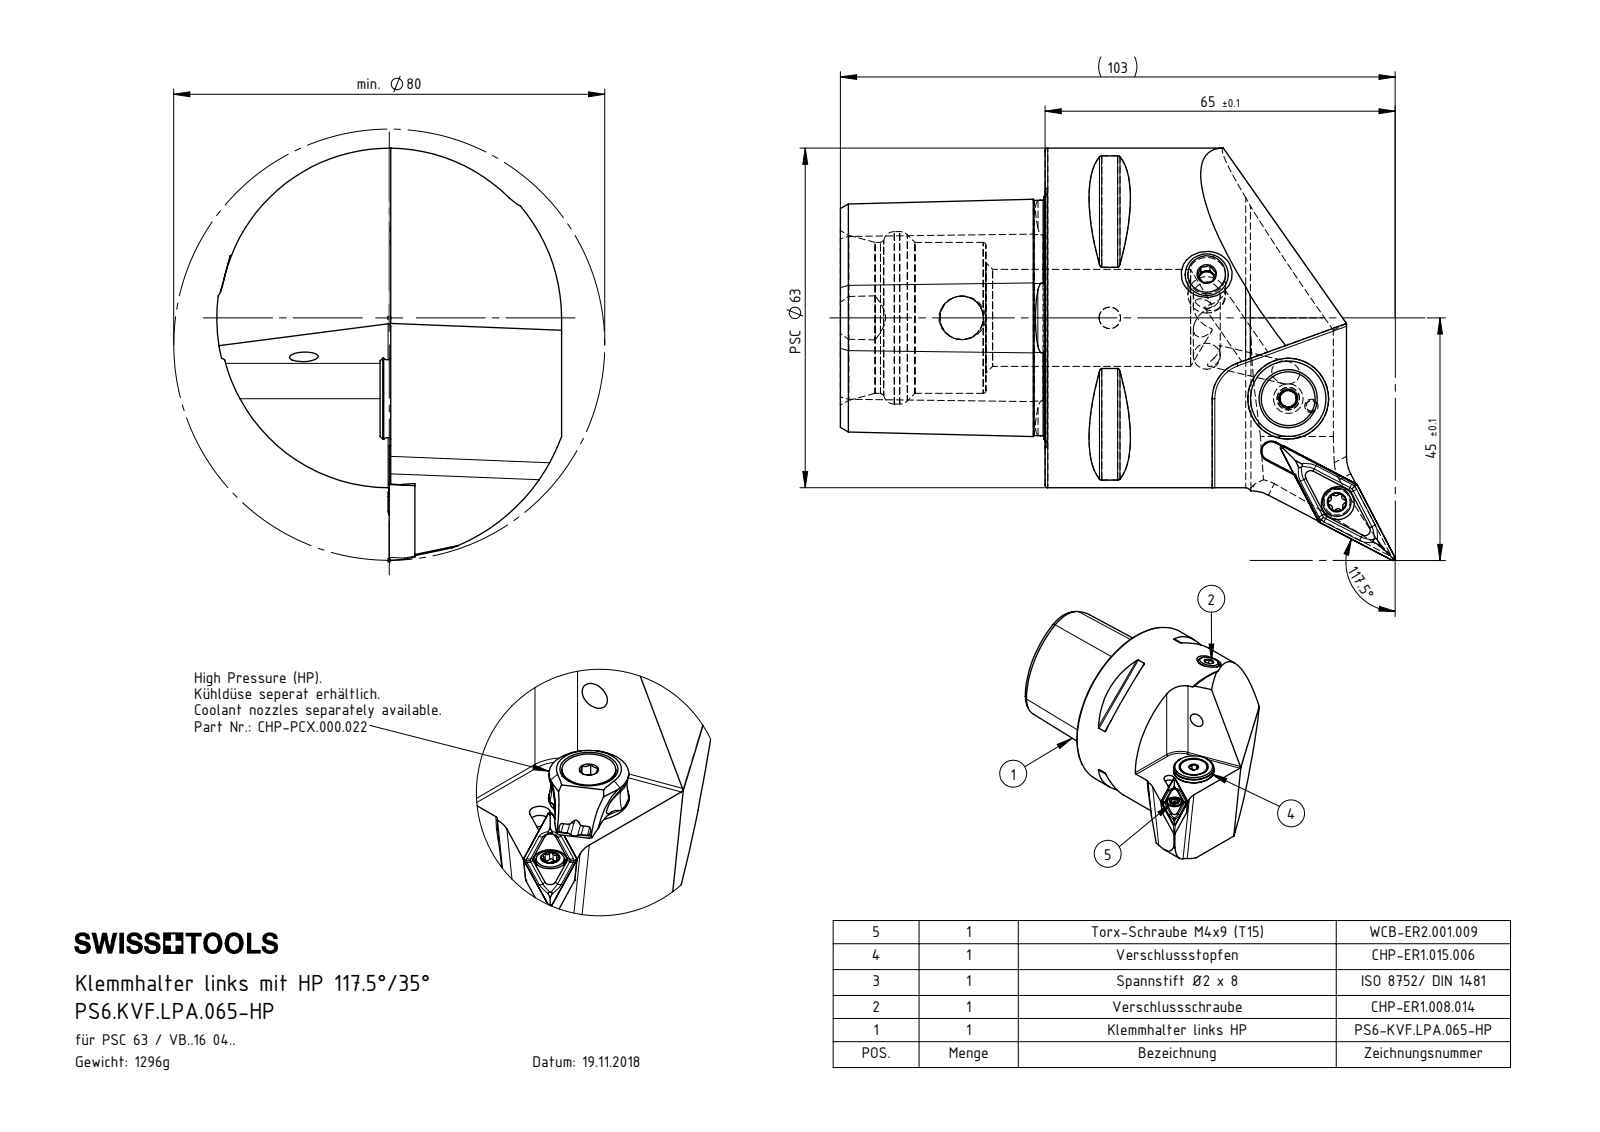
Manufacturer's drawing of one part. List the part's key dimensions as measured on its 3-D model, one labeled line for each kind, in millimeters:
Part name (STEP PRODUCT): PS6-KVF.LPA.065-HP_C; CHP-ER1.015.006; CHP-ER1.015.006_A; VBMT160404 (+6 more)
STEP written by: SolidWorks 2017 (AUTOMOTIVE_DESIGN)
Units: millimetres
Bodies: 8 solids, 384 faces (94 planar, 103 cylindrical, 187 other)
Overall size (bounding box): 103 × 76.5 × 64
Volume: 164 544 mm³ · Surface area: 31 108 mm²
Round holes (diameter × count): ⌀4.2 ×2, ⌀5 ×2, ⌀1.2 ×1, ⌀2 ×1, ⌀2.5 ×1, ⌀3 ×1, ⌀3.3 ×1, ⌀4 ×1, ⌀4.4 ×1, ⌀5.2 ×1, ⌀6.1 ×1, ⌀7 ×1
Round bosses / shafts (diameter × count): ⌀63 ×1, ⌀15 ×1, ⌀13.4 ×1, ⌀10 ×1, ⌀8 ×1, ⌀5.5 ×1, ⌀5.25 ×1, ⌀5 ×1
Partial cylindrical surfaces — rounded edges, fillets, slot ends (radius × count): R0.5 ×10, R0.34 ×6, R0.59 ×6, R7 ×3, R0.15 ×2, R1.75 ×1, R6 ×1, R32 ×1
Main face-to-face distances: 38, 31.7, 69, 31, 24.88, 27.24, 4.46, 27.2, 4.5, 27
Hole centre spacings: 4.5, 18.49, 18.67, 21.24, 21.44, 27.5, 36.36, 40.83
